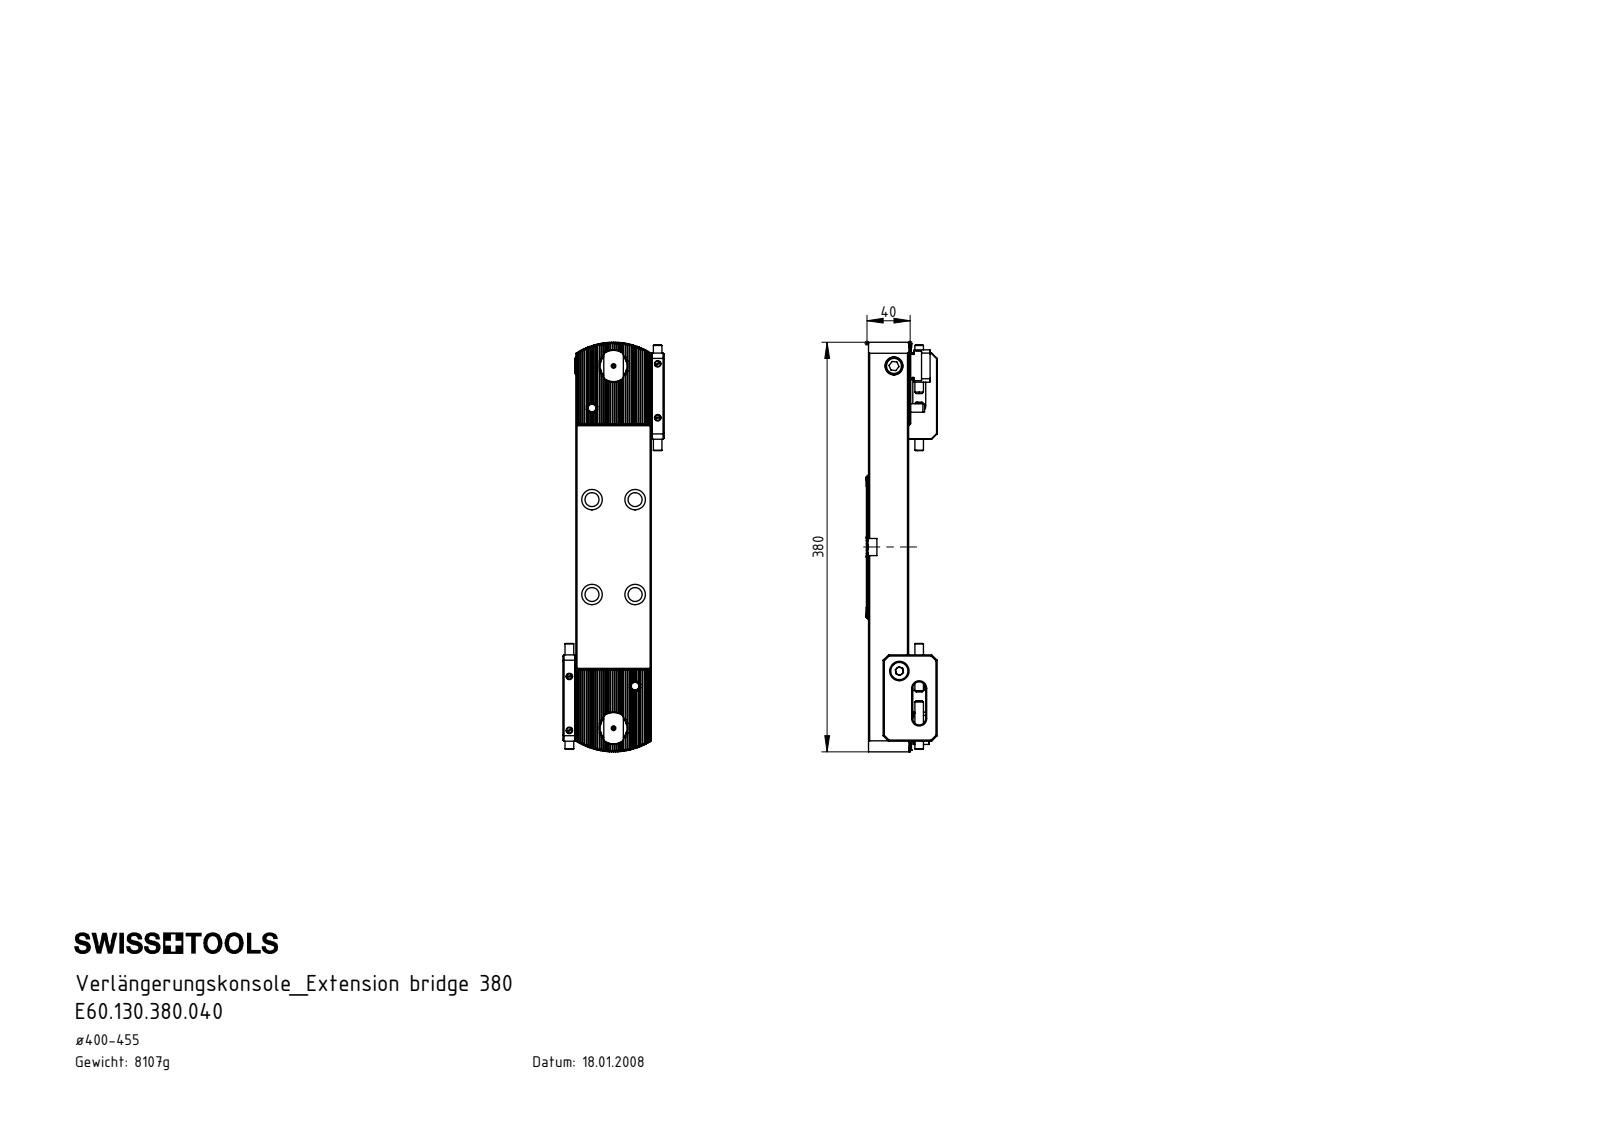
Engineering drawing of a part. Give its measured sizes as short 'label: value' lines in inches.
name: E60.130.380.040; VK1-ER3.001.028_A; VK1-ER7.001.012_mit langer Schraube; VK1-ER2.201.010_A_vorgespannt (+8 more)
written by: SolidWorks 2017 (CONFIG_CONTROL_DESIGN)
unit: in
bodies: 27 solids, 1563 faces (878 planar, 402 cylindrical, 283 other)
size: 14.961 × 3.701 × 2.582
volume: 63.4 in³; area: 257.6 in²
holes: 4× ⌀0.197, 4× ⌀0.236, 4× ⌀0.268, 4× ⌀0.512, 4× ⌀0.748, 2× ⌀0.079, 2× ⌀0.315, 2× ⌀0.335, 2× ⌀0.413, 2× ⌀0.433, 2× ⌀0.551, 2× ⌀0.709
bosses: 4× ⌀0.63, 4× ⌀0.236, 2× ⌀0.394, 2× ⌀0.315
rounds: 66× R0.006, 8× R0.079, 4× R0.236, 2× R0.484, 2× R0.591, 2× R2.559, 1× R0.313
face distances: 1.463, 2.756, 0.472, 3.228, 0.068, 0.341, 0.136, 0.273, 0.02, 1.637
hole spacings: 4.945, 8.383, 13.228, 0.311, 0.73, 0.772, 1.359, 1.381
